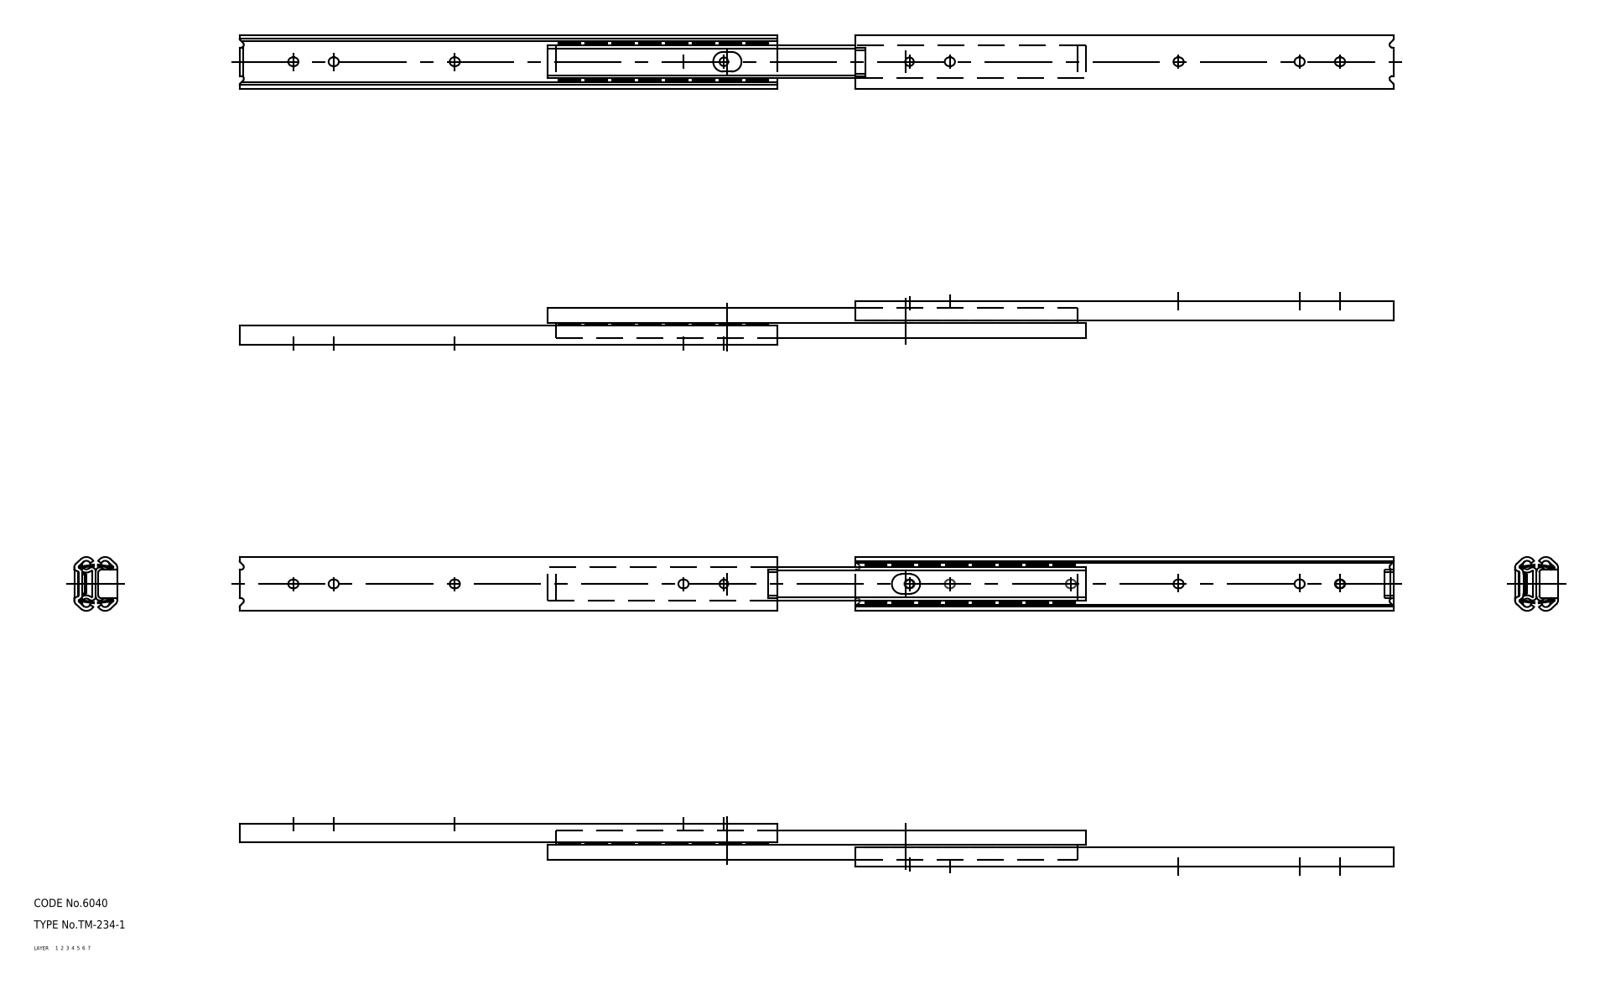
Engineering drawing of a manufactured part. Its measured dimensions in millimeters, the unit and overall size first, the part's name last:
Units: millimetres
Overall size (bounding box): 429 × 20 × 16
Volume: 26 501 mm³ · Surface area: 44 814 mm²
Bodies: 37 solids, 564 faces (0 planar, 0 cylindrical, 564 other)
Part name (STEP PRODUCT): ball; retainer; member_A; member_B (+1 more)
STEP written by: CADfix (AUTOMOTIVE_DESIGN)
